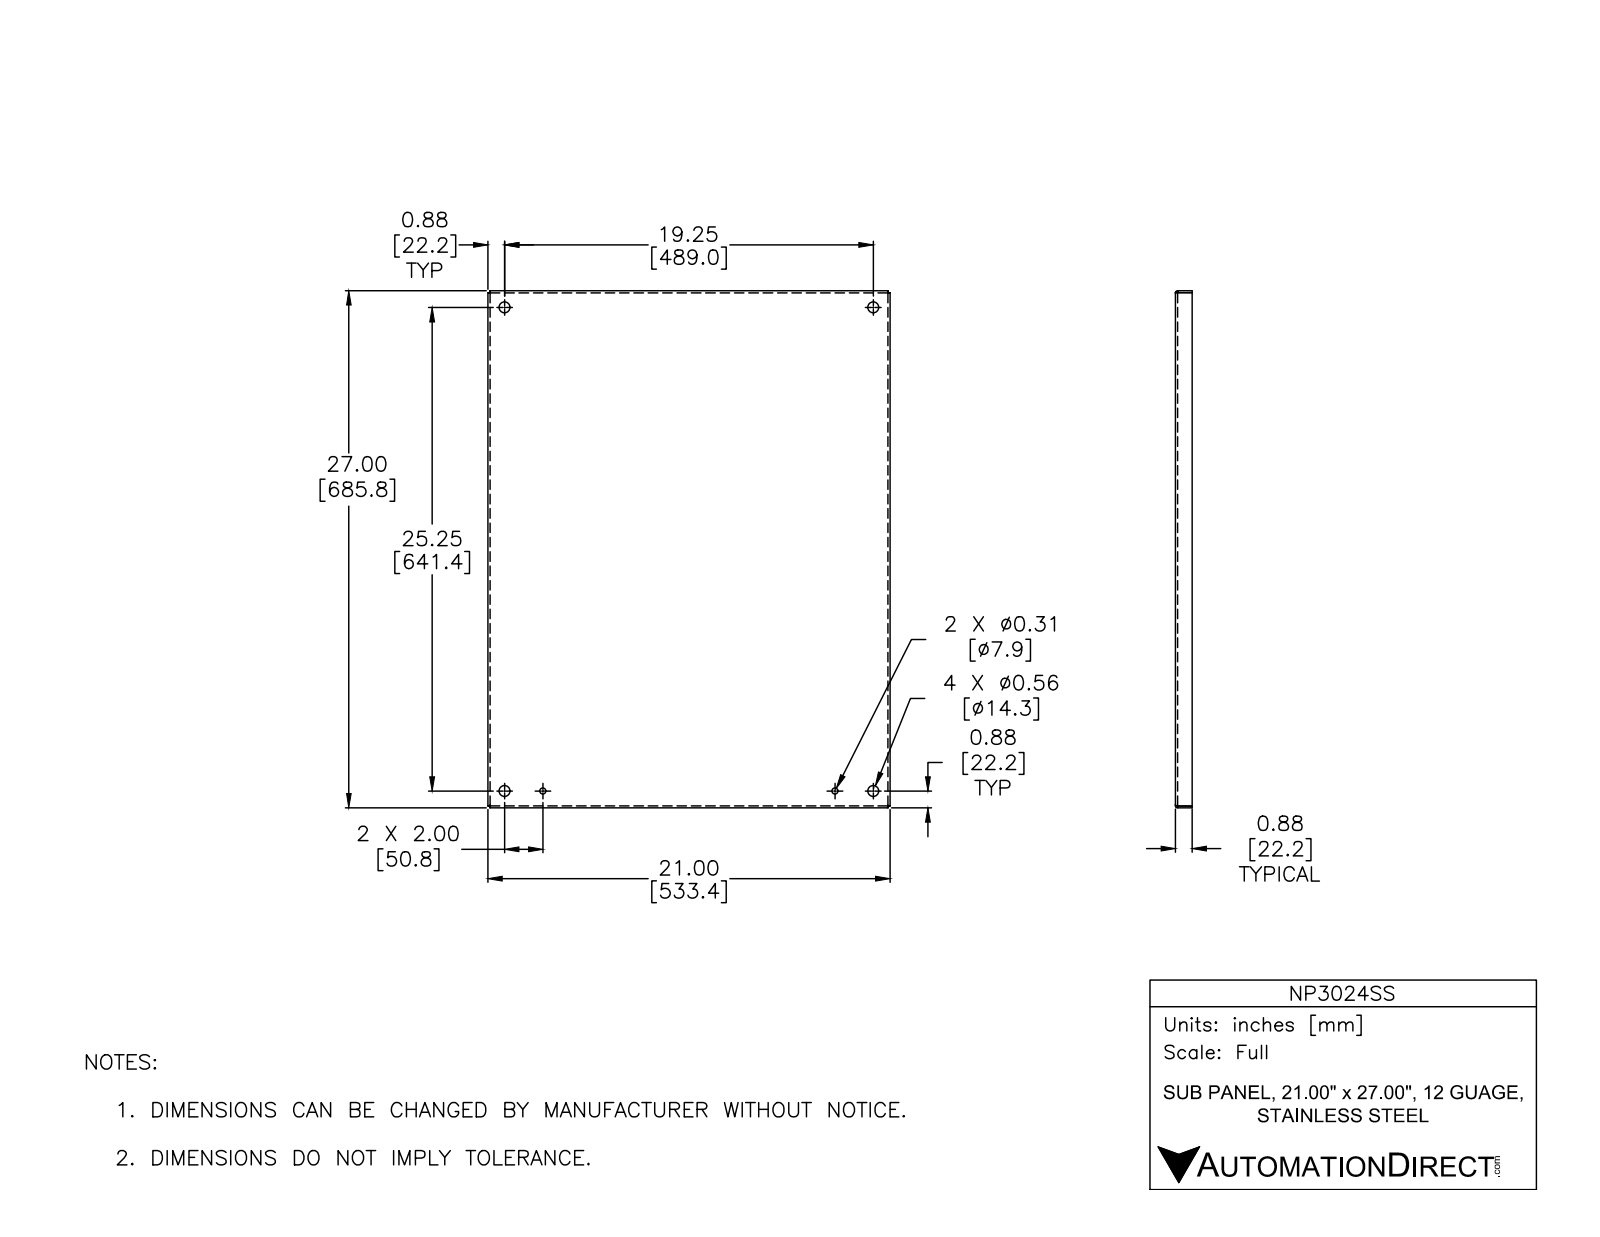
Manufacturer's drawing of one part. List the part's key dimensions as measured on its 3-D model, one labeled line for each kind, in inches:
Part name (STEP PRODUCT): NP3024SS
STEP written by: Autodesk Inventor 2012 (AUTOMOTIVE_DESIGN)
Units: inches
Bodies: 1 solid, 44 faces (22 planar, 14 cylindrical, 8 other)
Overall size (bounding box): 27 × 21 × 0.875
Volume: 59.68 in³ · Surface area: 1 284 in²
Round holes (diameter × count): ⌀0.563 ×4, ⌀0.312 ×2
Partial cylindrical surfaces — rounded edges, fillets, slot ends (radius × count): R0.031 ×4, R0.125 ×4
Main face-to-face distances: 0.094, 20.906, 26.906, 21, 20.813, 26.813, 27, 0.781, 0.875, 0.105
Hole centre spacings: 19.25, 25.25, 25.329, 30.58, 31.752, 2, 2, 15.25
